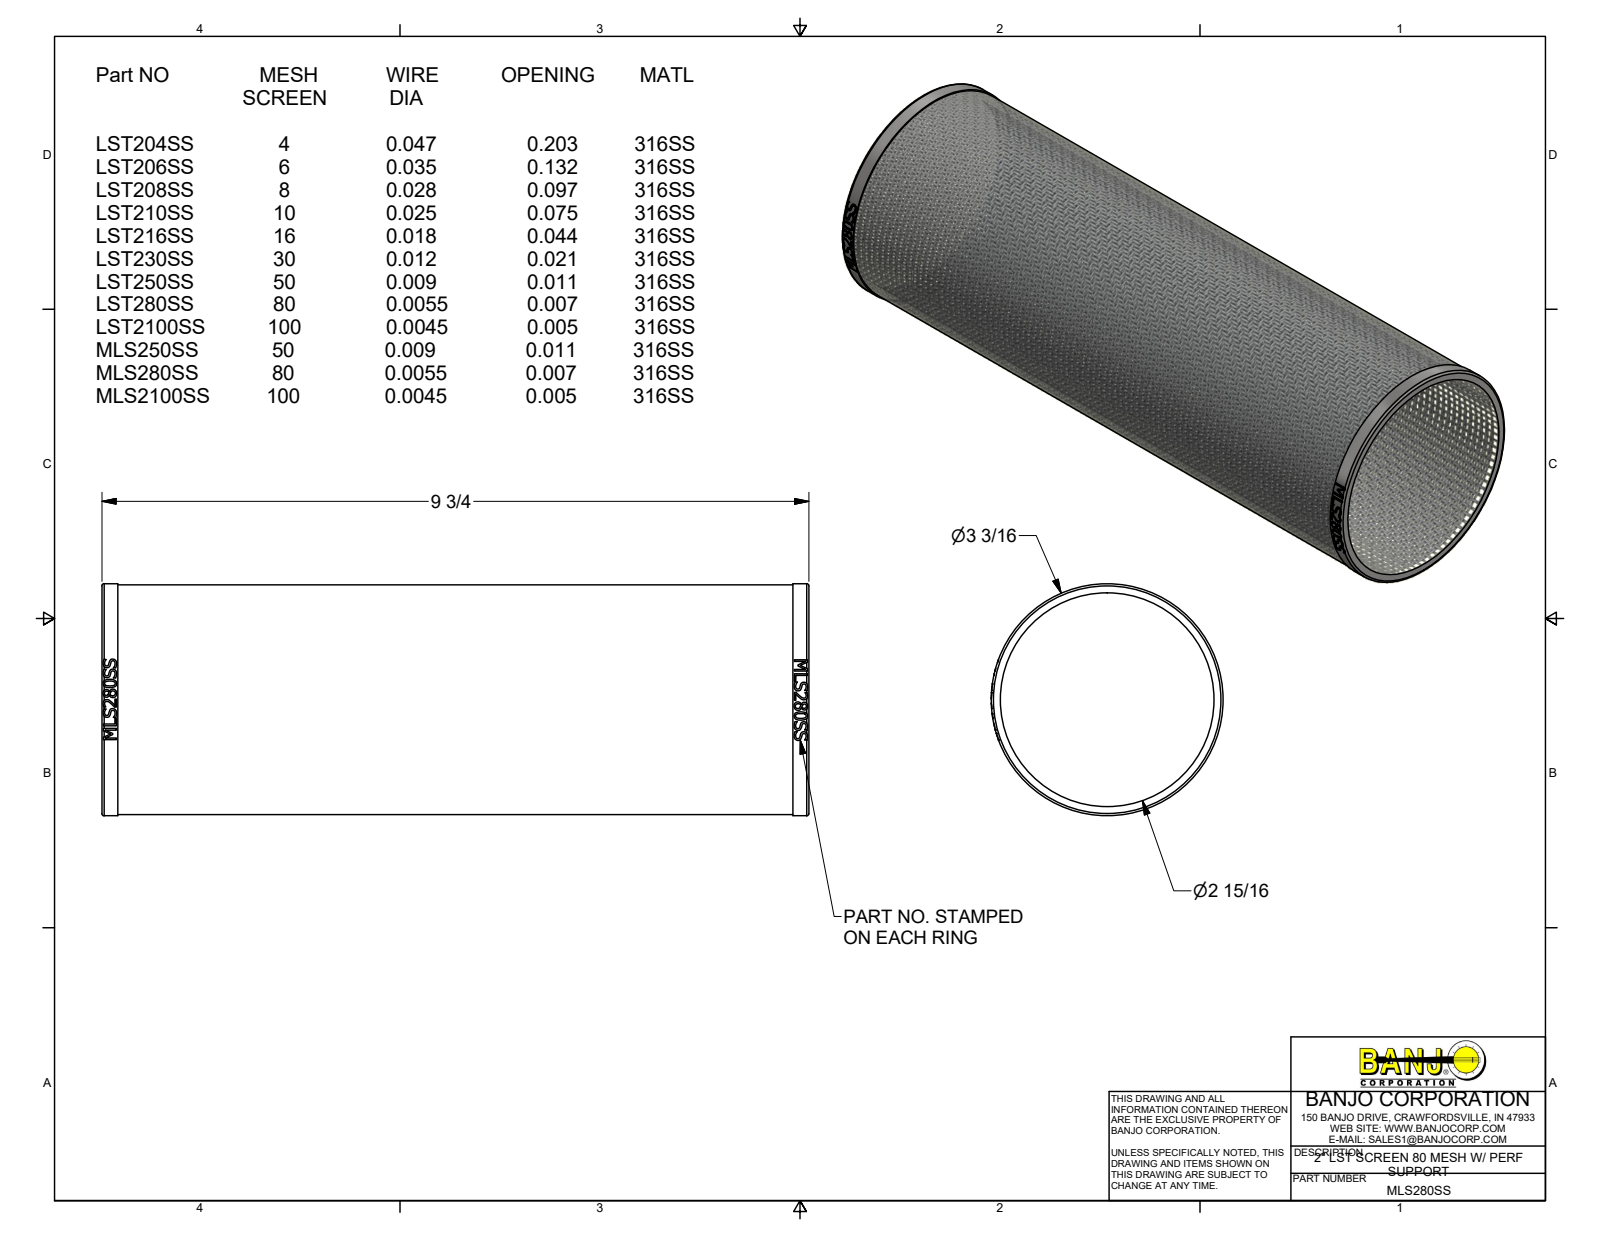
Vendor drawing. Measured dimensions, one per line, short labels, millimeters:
name: MLS280SS
written by: Autodesk Inventor 2017 (AUTOMOTIVE_DESIGN)
unit: mm
bodies: 1 solid, 296 faces (84 planar, 30 cylindrical, 182 other)
size: 246.89 × 80.97 × 80.97
volume: 161 615 mm³; area: 239 830 mm²
holes: 1× ⌀74.61, 1× ⌀79.71
bosses: 1× ⌀80.98, 1× ⌀80.21, 1× ⌀79.45
rounds: 1× R39.98
face distances: 246.89, 241.33, 5.56, 235.77, 19.08, 1.53, 0.61, 0.49, 5.07, 3.92
